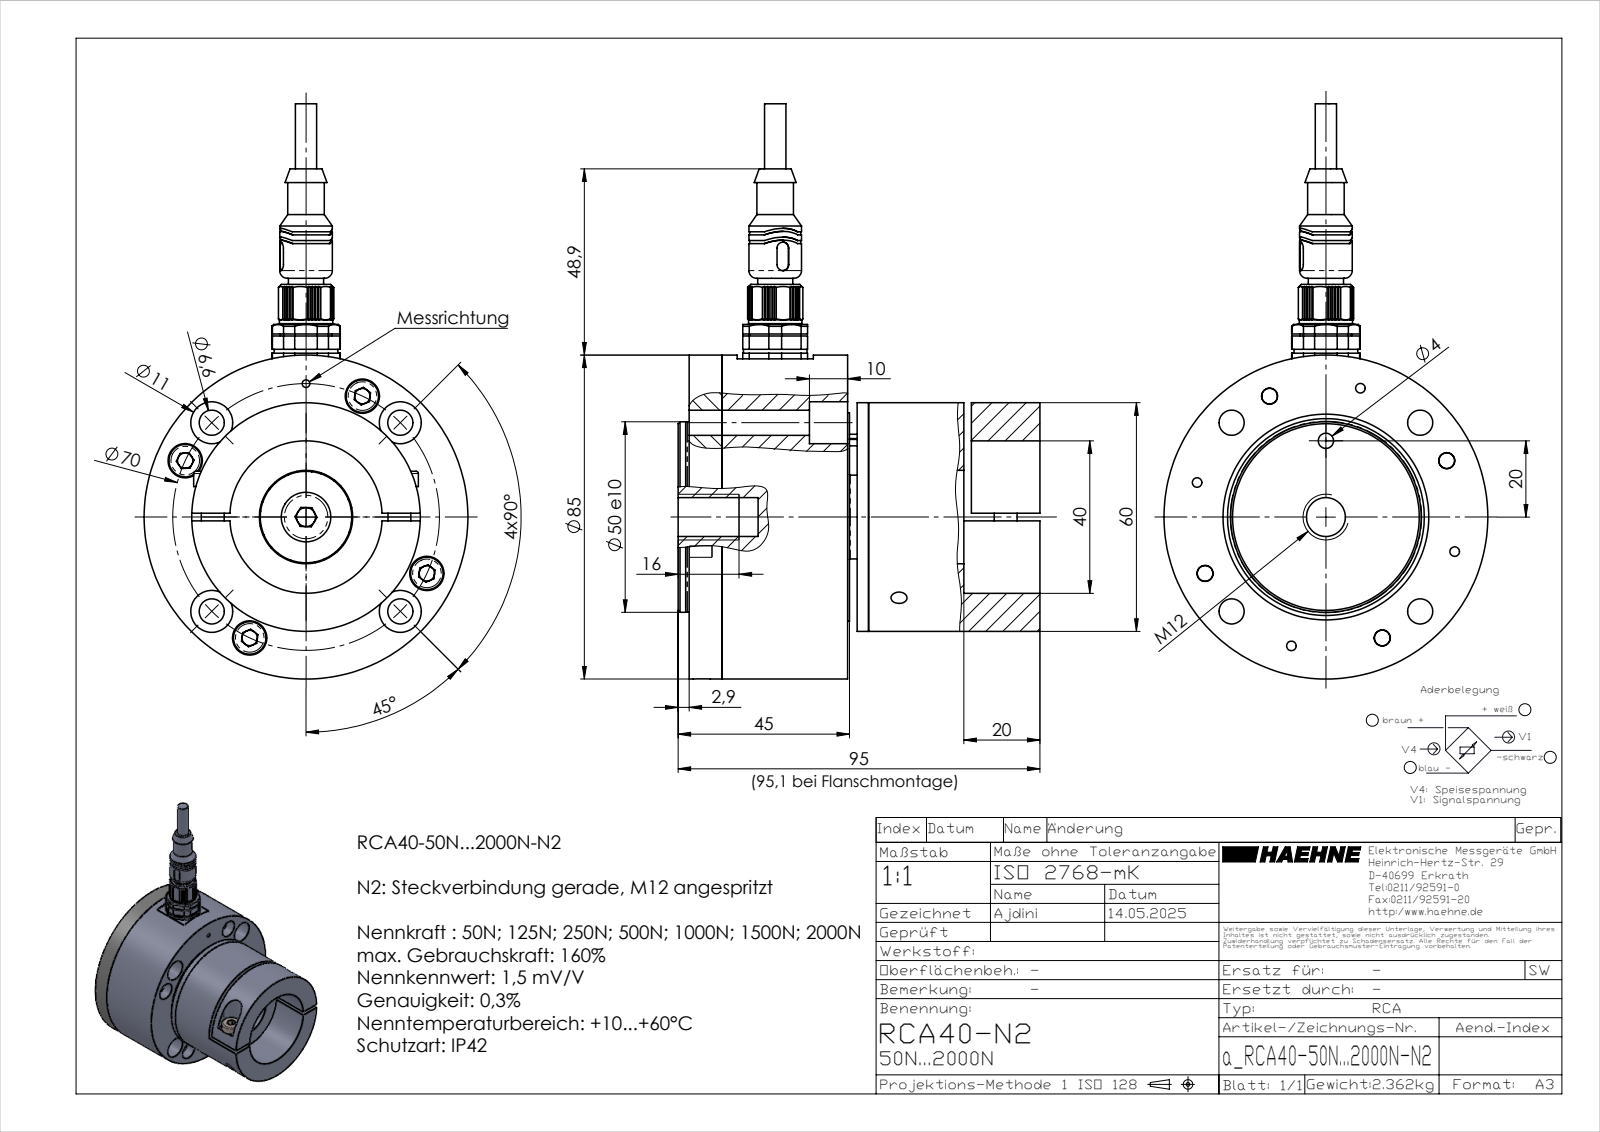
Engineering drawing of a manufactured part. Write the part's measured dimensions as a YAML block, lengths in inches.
part_name: "inafag_1203-tvh_7zkvytp7yxkimpdvw8sj0b5w4_12; inafag_1203-tvh_7zkvytp7yxkimpdvw8sj0b5w4_16; inafag_1203-tvh_7zkvytp7yxkimpdvw8sj0b5w4_04; DIN EN ISO 8747-M3x10-St_DIN EN ISO 8747-M3x10-St (+8 more)"
step_written_by: "SolidWorks 2023 (AUTOMOTIVE_DESIGN)"
units: inches
bodies: {solids: 53, faces: 1169, planar: 647, cylindrical: 300, other: 222}
overall_size: [5.942, 3.744, 3.346]
volume: 21.44
surface_area: 173.9
round_holes:
  - {diameter: 0.134, count: 9}
  - {diameter: 0.098, count: 8}
  - {diameter: 0.26, count: 6}
  - {diameter: 0.165, count: 5}
  - {diameter: 0.433, count: 5}
  - {diameter: 0.043, count: 4}
  - {diameter: 0.045, count: 4}
  - {diameter: 0.063, count: 4}
  - {diameter: 0.073, count: 4}
  - {diameter: 0.157, count: 4}
  - {diameter: 0.209, count: 4}
  - {diameter: 0.354, count: 4}
round_bosses_or_shafts:
  - {diameter: 0.118, count: 9}
  - {diameter: 0.224, count: 8}
  - {diameter: 0.335, count: 4}
  - {diameter: 0.197, count: 4}
  - {diameter: 0.071, count: 4}
  - {diameter: 0.061, count: 4}
  - {diameter: 0.059, count: 4}
  - {diameter: 0.039, count: 4}
partial_cylinders:
  - {radius: 0.008, count: 16}
  - {radius: 0.012, count: 10}
  - {radius: 0.016, count: 4}
  - {radius: 0.021, count: 4}
  - {radius: 0.039, count: 4}
  - {radius: 0.05, count: 4}
  - {radius: 0.472, count: 4}
  - {radius: 0.063, count: 2}
face_to_face_distances: [0.118, 0.339, 1.854, 0.079, 0.457, 1.181, 1.398, 1.772, 1.972, 1.516]
hole_center_spacings: [1.378, 1.949, 0.976, 0.992, 1.291, 2.013, 2.223, 0.098]
